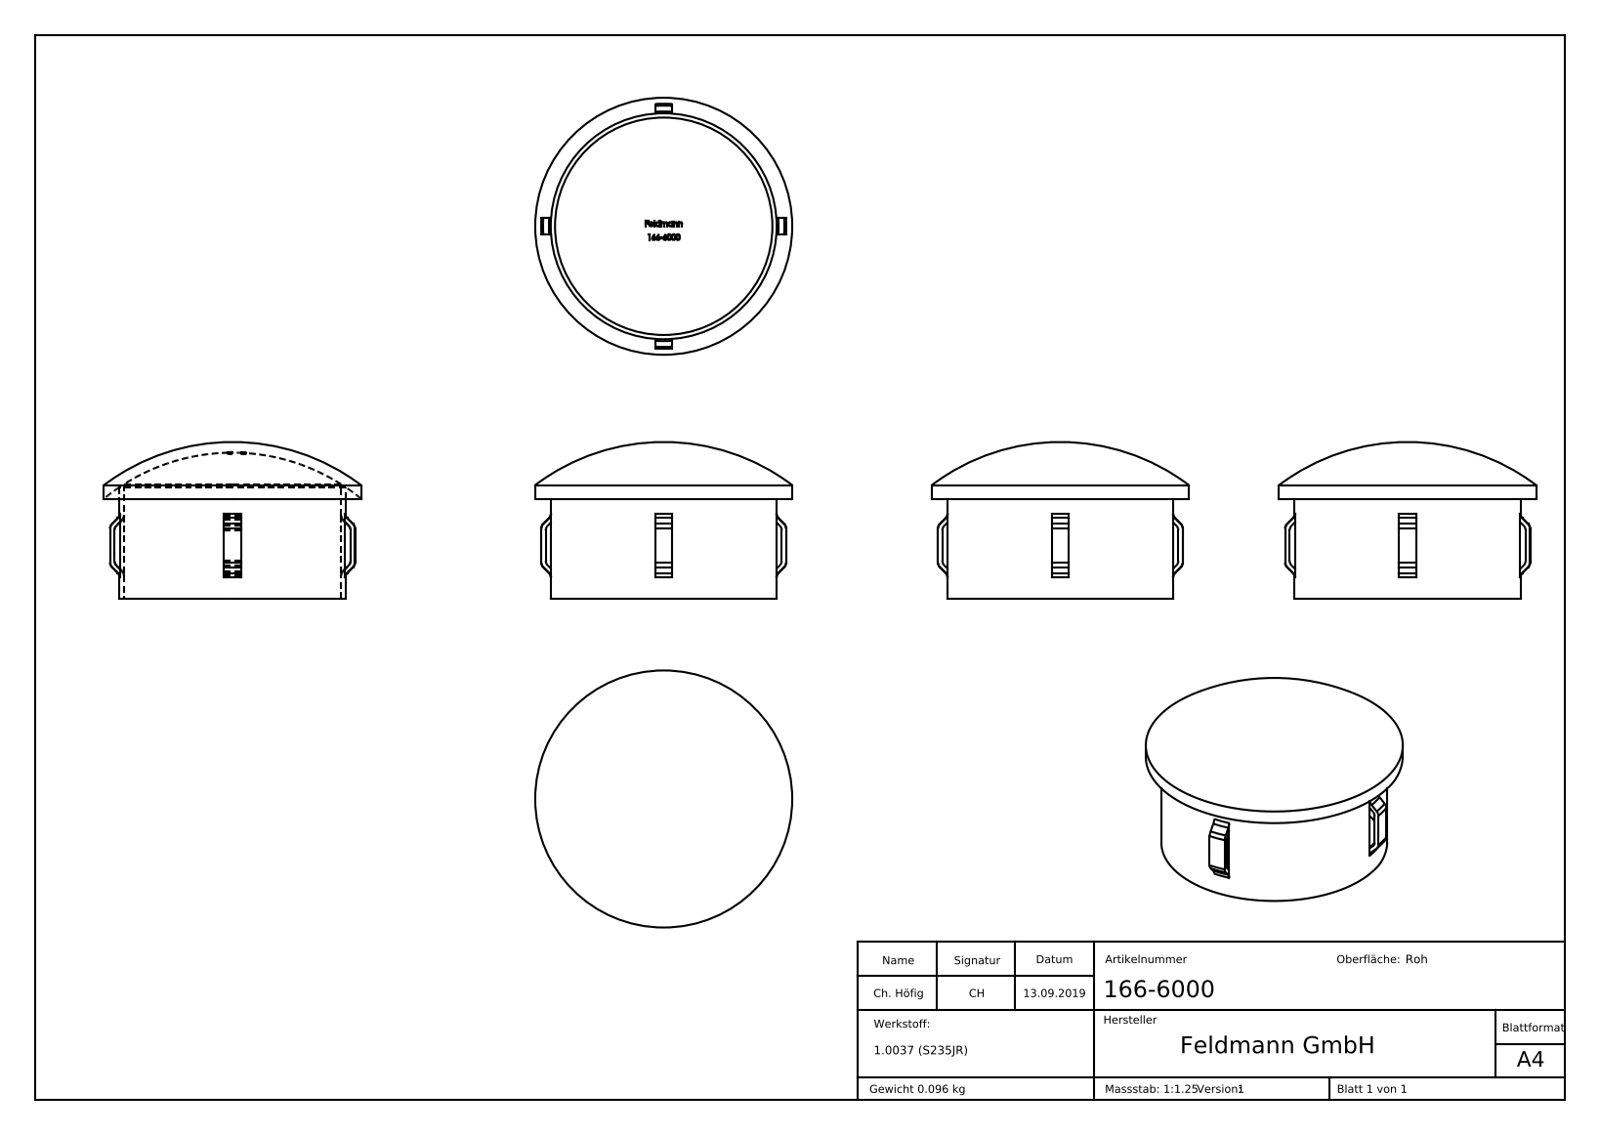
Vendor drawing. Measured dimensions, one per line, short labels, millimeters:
name: 166-6000
written by: SolidWorks 2015 (CONFIG_CONTROL_DESIGN)
unit: mm
bodies: 1 solid, 308 faces (90 planar, 16 cylindrical, 202 other)
size: 60.3 × 60.3 × 36.8
volume: 12 363 mm³; area: 15 910 mm²
holes: 1× ⌀51
bosses: 1× ⌀60.3, 1× ⌀53
rounds: 1× R27.75, 1× R28.75
face distances: 4, 2.97, 1.26, 2, 0.39, 3.27, 0.87, 1.36, 2.28, 0.99
